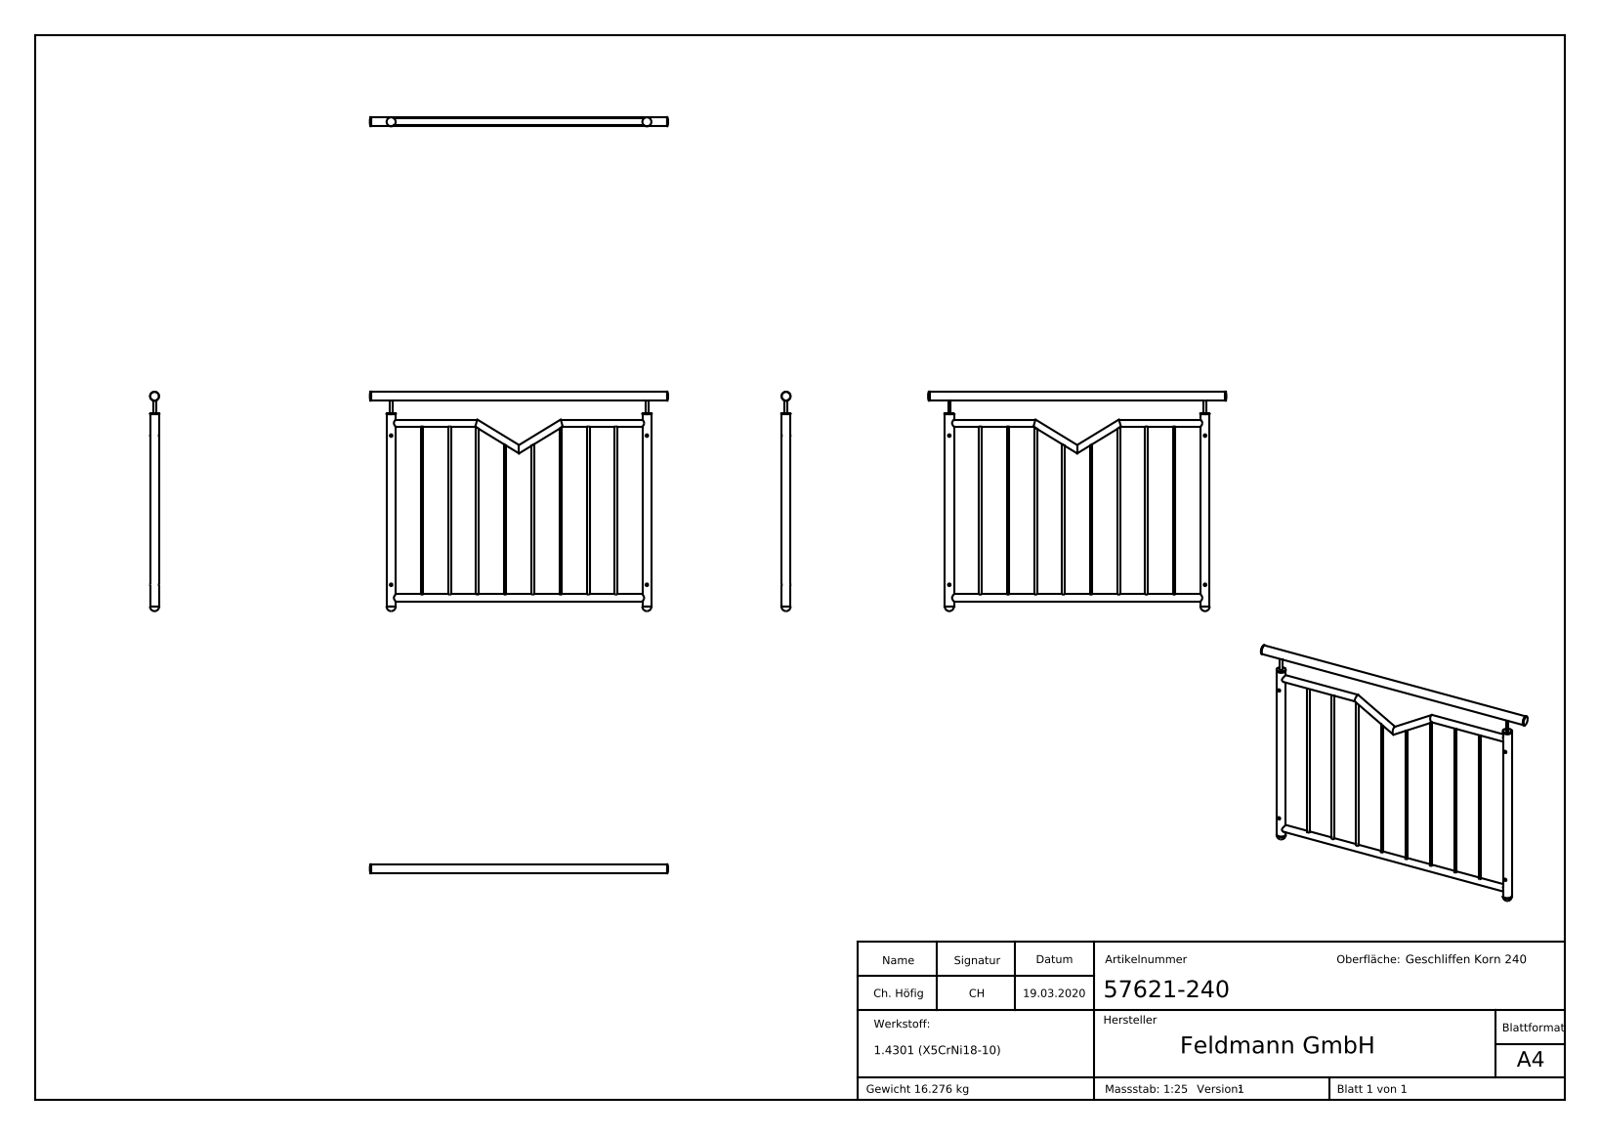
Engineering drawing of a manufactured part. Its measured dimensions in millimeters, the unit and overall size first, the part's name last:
Units: millimetres
Overall size (bounding box): 16102.4 × 8000 × 8000
Round holes (diameter × count): ⌀12 ×4, ⌀29.7 ×4, ⌀38.4 ×3, ⌀6.8 ×2, ⌀34.5 ×2, ⌀34.6 ×1
Round bosses / shafts (diameter × count): ⌀12 ×10, ⌀33.7 ×4, ⌀42.4 ×3, ⌀37.5 ×3, ⌀8 ×2, ⌀6 ×2
Partial cylindrical surfaces — rounded edges, fillets, slot ends (radius × count): R2 ×4, R19.4 ×3, R17.35 ×2, R19.3 ×1
Main face-to-face distances: 13, 5, 8, 890.6, 898.6, 903.6, 18.7, 18.75, 1386, 18.76
Hole centre spacings: 1200, 700, 1389.24, 126.2, 820, 946.2
Volume: 2 060 000 mm³ · Surface area: 1 563 000 mm²
Bodies: 10 solids, 6675 faces (3206 planar, 1045 cylindrical, 2424 other)
Part name (STEP PRODUCT): Stopfen Konfig; 576XX-240 Teil2; 50236-240-60; 576XX-240 Teil1 (+7 more)
STEP written by: SolidWorks 2015 (CONFIG_CONTROL_DESIGN)
